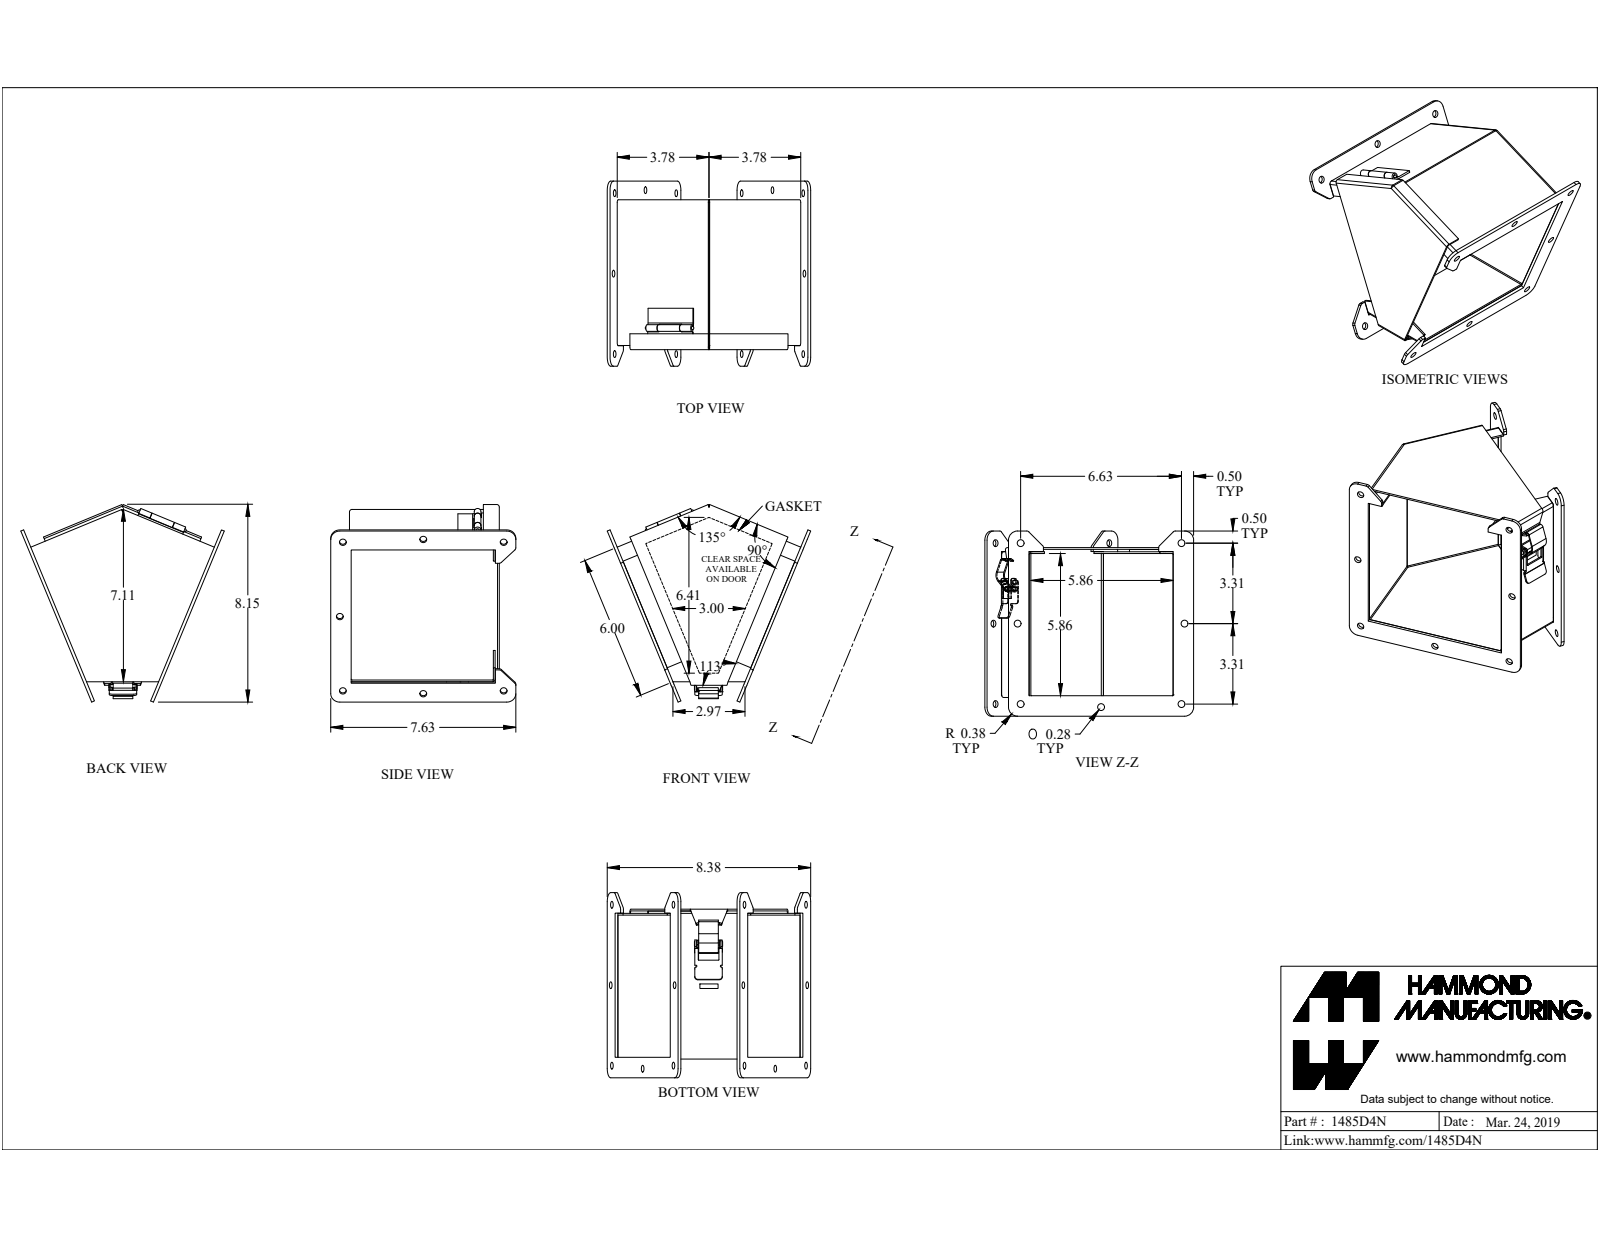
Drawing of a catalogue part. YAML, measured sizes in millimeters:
part_name: "1485D4N"
step_written_by: "SolidWorks 2019 (CONFIG_CONTROL_DESIGN)"
units: millimeters
bodies: {solids: 10, faces: 286, planar: 165, cylindrical: 109, other: 12}
overall_size: [212.9, 206.7, 193.7]
volume: 248800
surface_area: 253200
round_holes:
  - {diameter: 7.1, count: 14}
  - {diameter: 3.2, count: 2}
  - {diameter: 3.3, count: 1}
  - {diameter: 4.2, count: 1}
round_bosses_or_shafts:
  - {diameter: 7, count: 2}
  - {diameter: 4.7, count: 2}
  - {diameter: 4, count: 1}
  - {diameter: 3.2, count: 1}
  - {diameter: 3.2, count: 1}
partial_cylinders:
  - {radius: 3.2, count: 11}
  - {radius: 0.9, count: 10}
  - {radius: 2.7, count: 10}
  - {radius: 9.5, count: 8}
  - {radius: 0.4, count: 7}
  - {radius: 0.9, count: 3}
  - {radius: 1, count: 3}
  - {radius: 1.9, count: 3}
face_to_face_distances: [1.8, 154.9, 3.2, 156.8, 153.1, 4.4, 150.6, 6.2, 148.7, 2.5]
hole_center_spacings: [191, 168.3, 84.2, 84.2, 123.5, 238, 27.4, 57.1]
